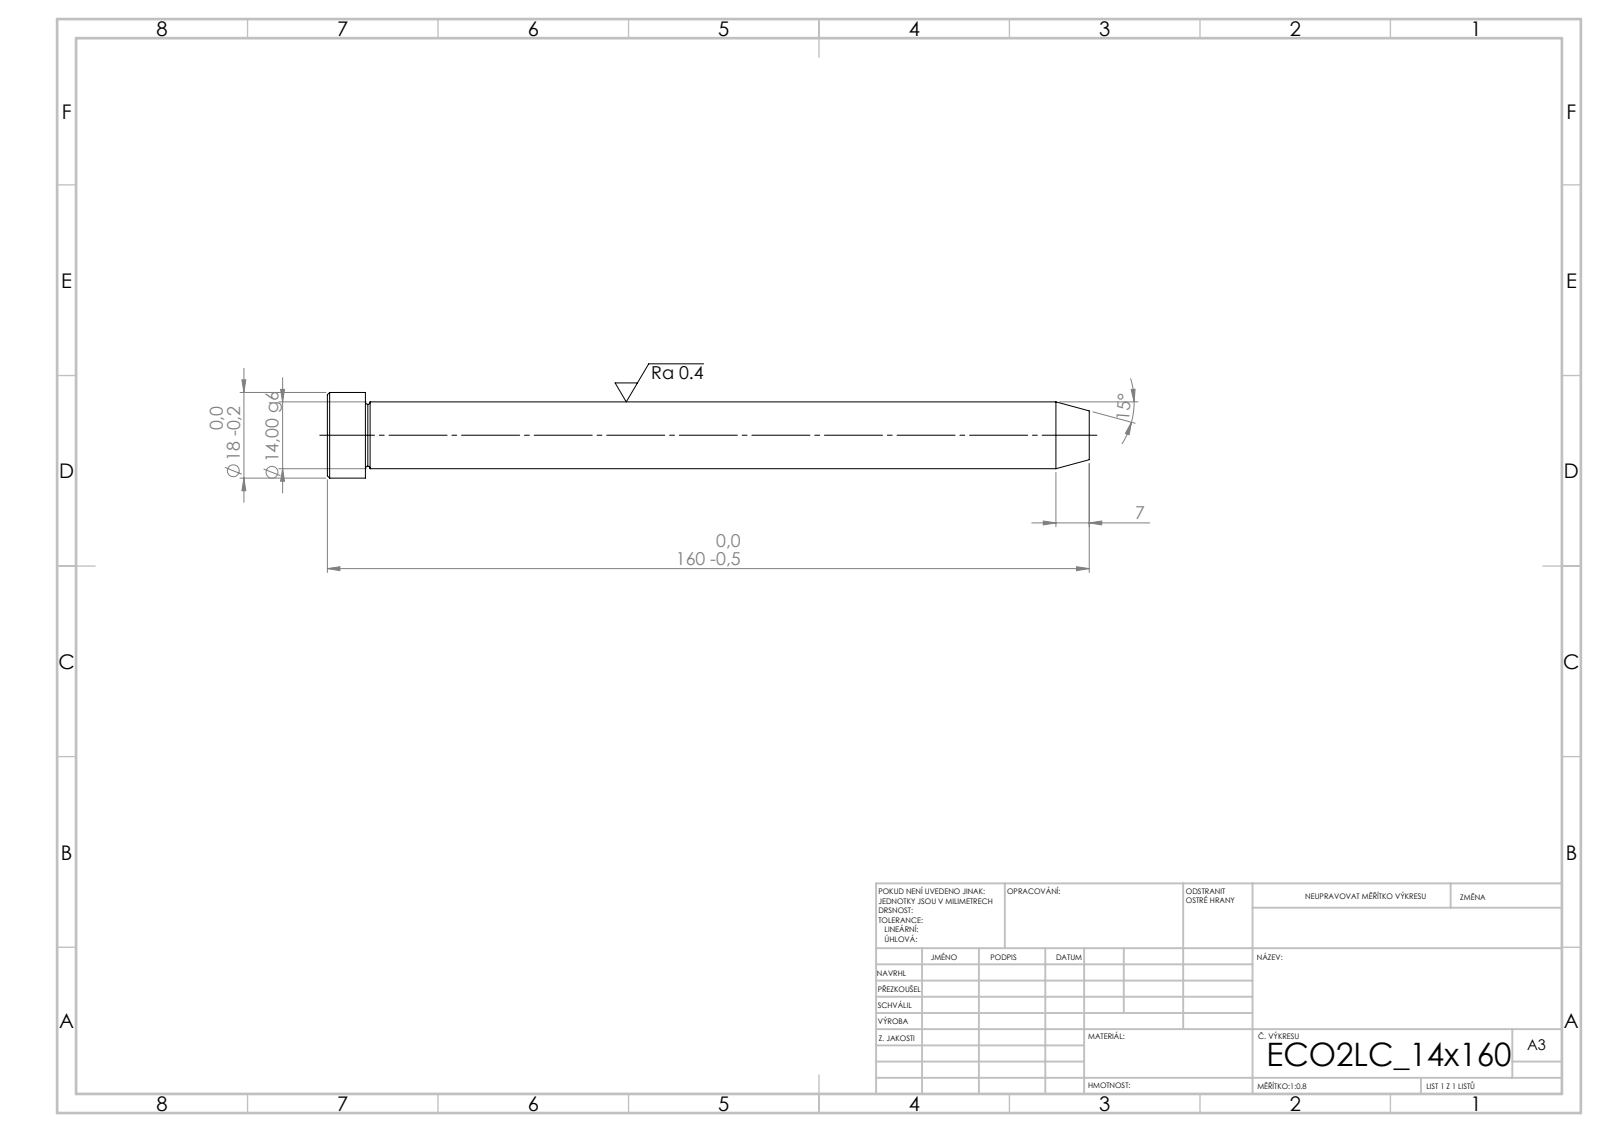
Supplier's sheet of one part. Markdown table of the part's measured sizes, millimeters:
| quantity | value |
| --- | --- |
| STEP written by | SolidWorks 2019 (CONFIG_CONTROL_DESIGN) |
| units | millimeters |
| bodies | 1 solid, 15 faces (3 planar, 4 cylindrical, 8 other) |
| overall size | 160 × 18 × 18 |
| volume | 25 148 mm³ |
| surface area | 7 548 mm² |
| round bosses / shafts (diameter × count) | 18 × 1, 14 × 1 |
| main face-to-face distances | 8, 152, 160 |
